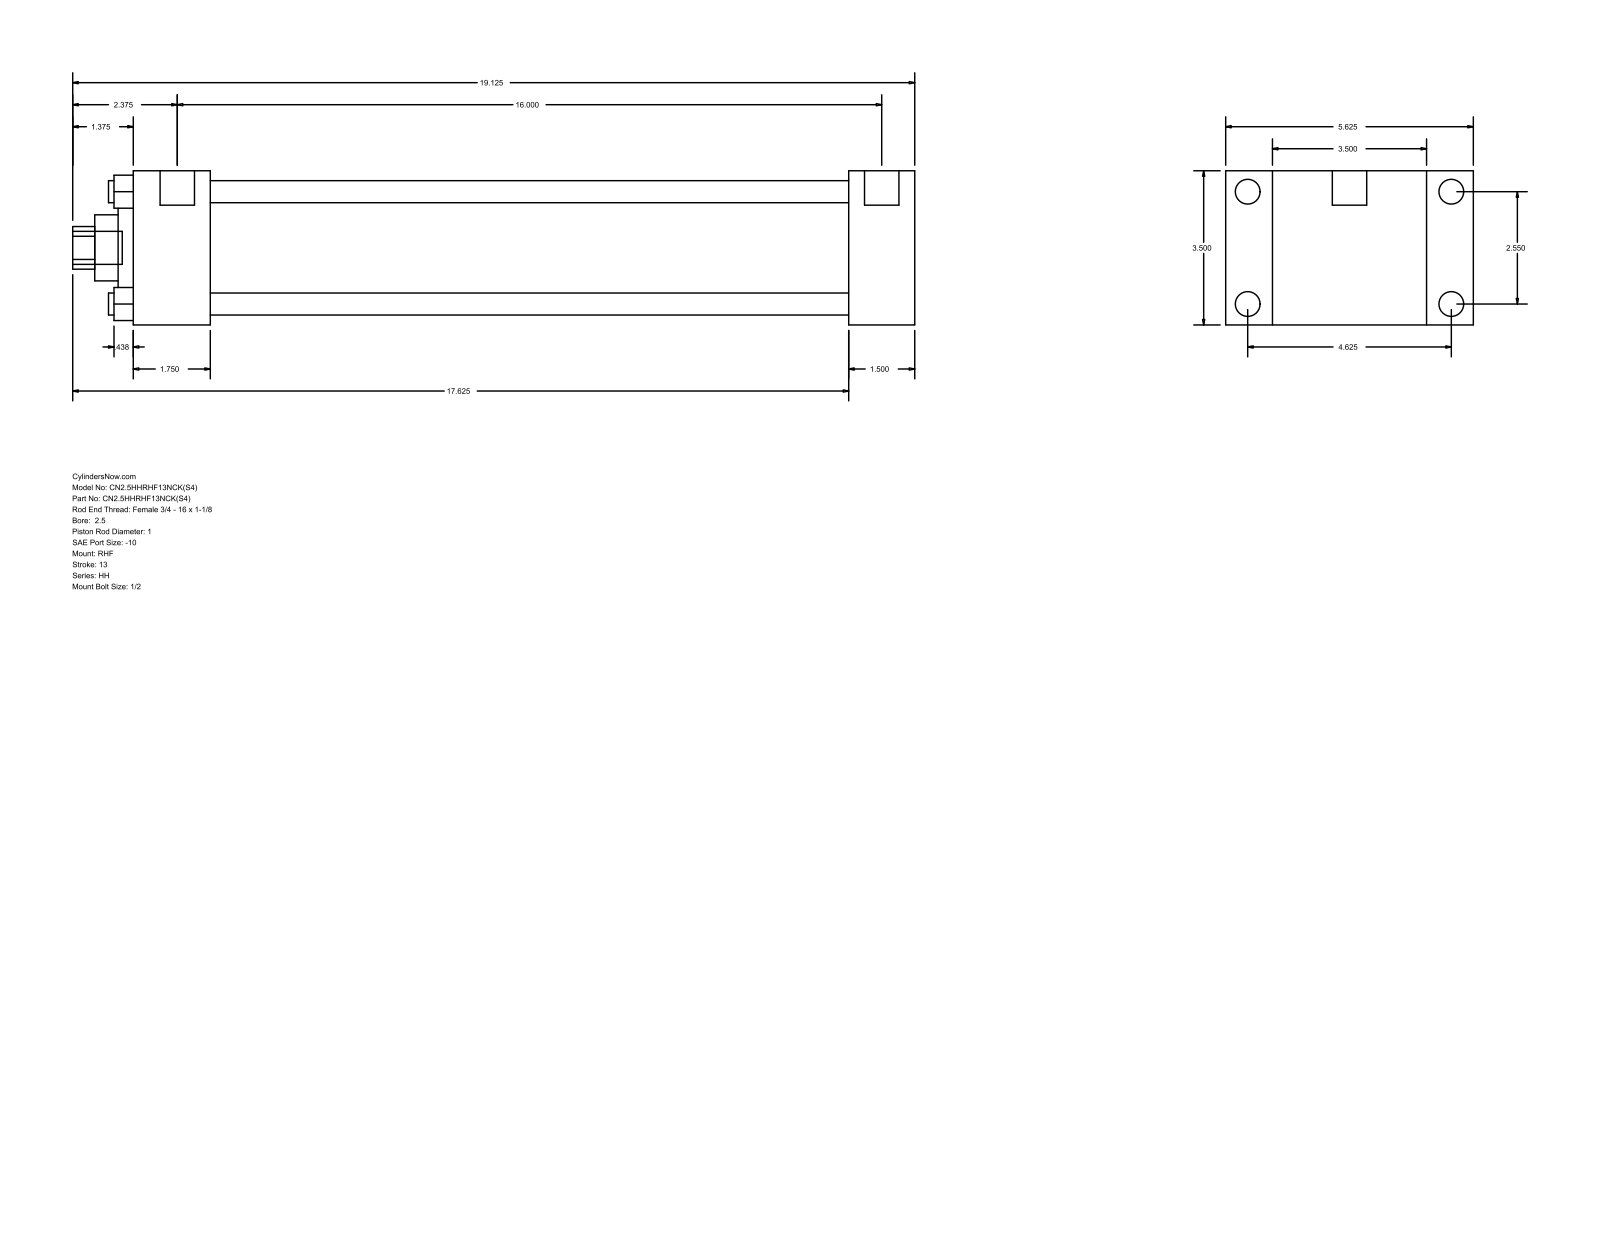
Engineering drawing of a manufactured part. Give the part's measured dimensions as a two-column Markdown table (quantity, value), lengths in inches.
| quantity | value |
| --- | --- |
| part name | HH_RHF__0250_1 |
| STEP written by | GSSL Pune (CONFIG_CONTROL_DESIGN) |
| units | inches |
| bodies | 0 solids, 90 faces (61 planar, 29 cylindrical, 0 other) |
| overall size | 19.125 × 5.625 × 3.5 |
| round holes (diameter × count) | 0.5 × 4, 1 × 1, 1.5 × 1, 2.375 × 1, 2.875 × 1 |
| round bosses / shafts (diameter × count) | 0.563 × 4, 0.219 × 4, 0.781 × 2, 0.75 × 1 |
| partial cylindrical surfaces (radius × count) | 0.484 × 1 |
| main face-to-face distances | 3.5, 1.5, 1.063, 4.563, 16.25, 17.75, 5.625, 1.75, 14.5, 16 |
| hole center spacings | 1.803, 2.55, 3.606 |
